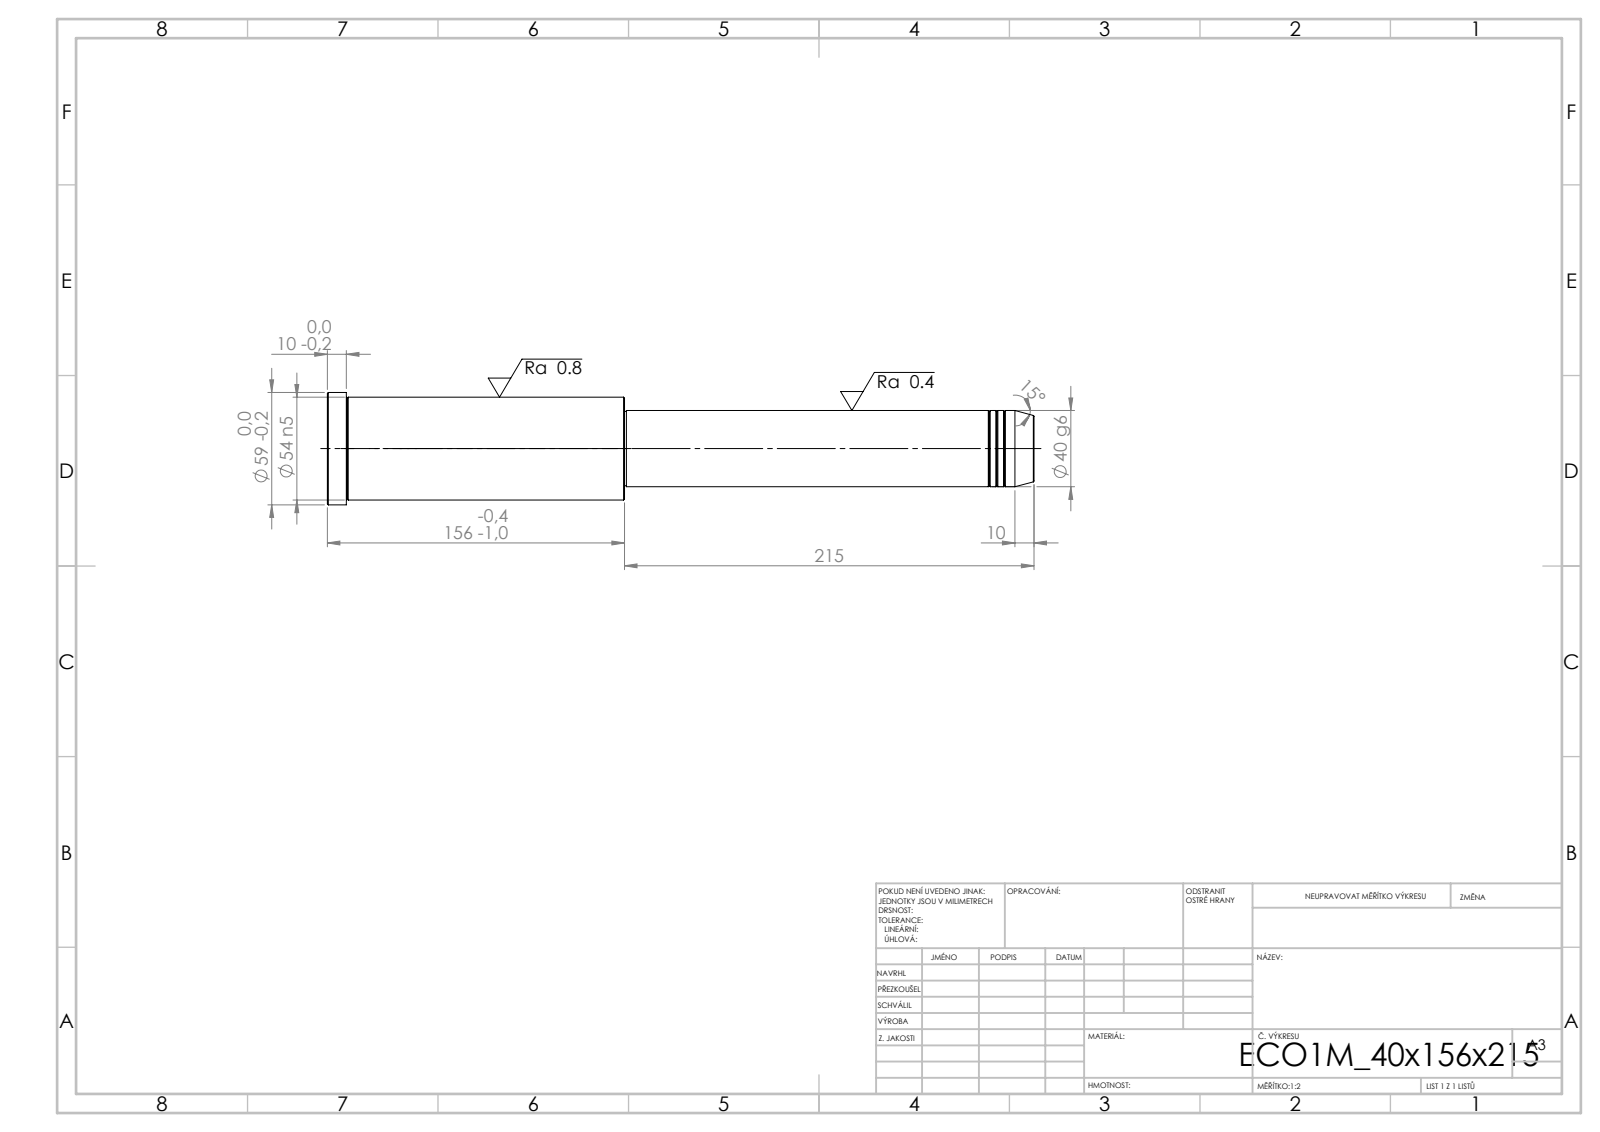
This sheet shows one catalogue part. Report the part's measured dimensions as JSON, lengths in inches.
{"step_written_by": "SolidWorks 2019 (CONFIG_CONTROL_DESIGN)", "units": "inches", "bodies": {"solids": 1, "faces": 43, "planar": 5, "cylindrical": 14, "other": 24}, "overall_size": [14.606, 2.323, 2.323], "volume_in3": 38.44, "surface_area_in2": 91.53, "round_bosses_or_shafts": [[2.323, 1], [2.126, 1], [1.575, 1], [1.535, 1]], "face_to_face_distances": [6.142, 8.465, 14.606, 14.213, 5.748, 0.394, 8.425, 0.039, 5.787, 6.181]}
